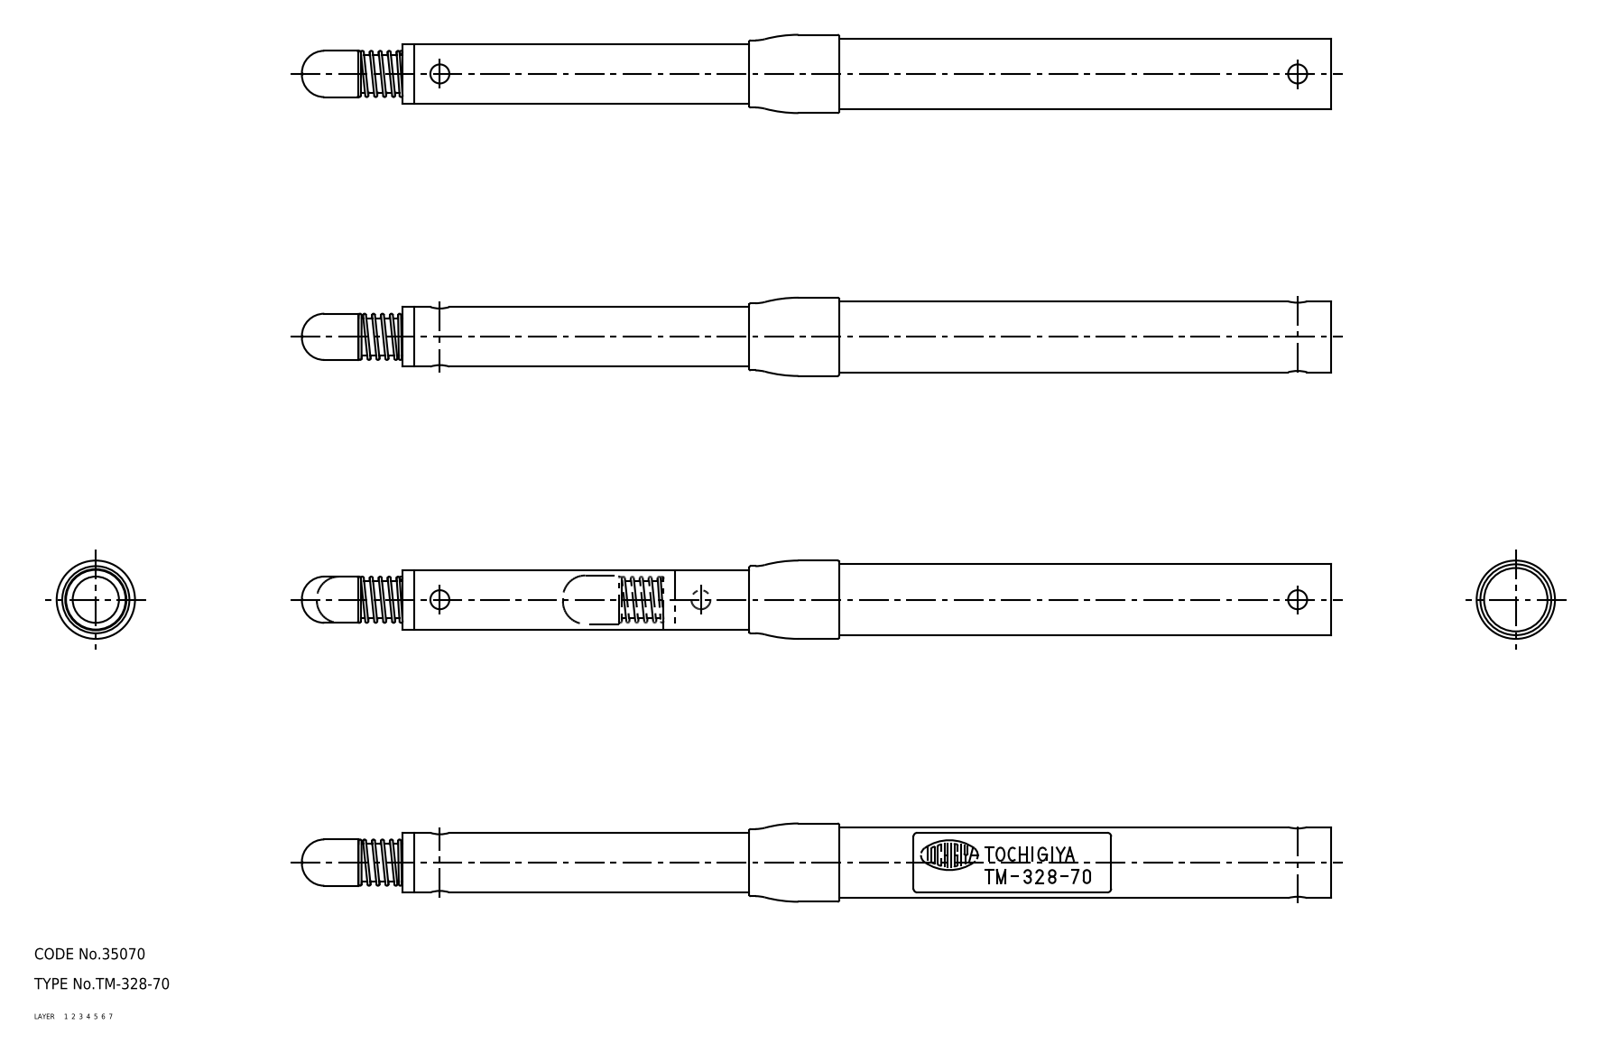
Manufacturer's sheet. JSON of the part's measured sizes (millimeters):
{"part_name": "67112534; 67112547; 67112561", "step_written_by": "CADfix (AUTOMOTIVE_DESIGN)", "units": "millimeters", "bodies": {"solids": 2, "faces": 45, "planar": 0, "cylindrical": 0, "other": 45}, "overall_size": [276, 21, 21], "volume_mm3": 65782, "surface_area_mm2": 17100}
